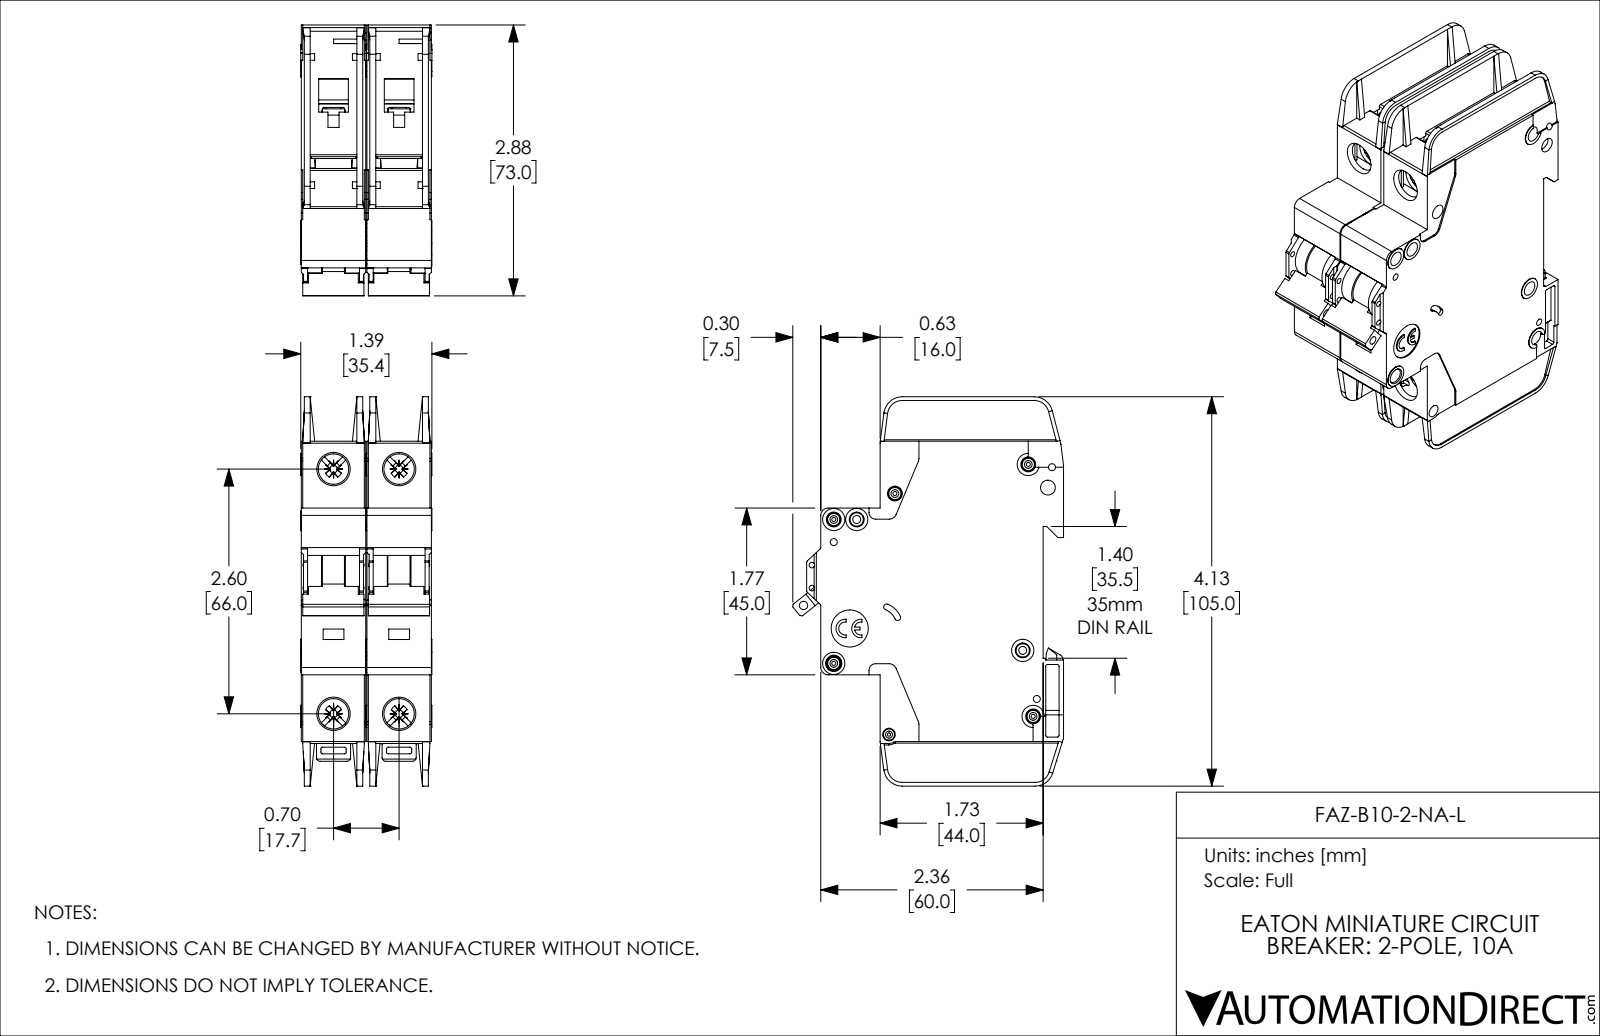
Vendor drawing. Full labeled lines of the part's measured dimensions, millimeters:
Part name (STEP PRODUCT): FAZ-B10-2-NA-L
STEP written by: SolidWorks 2019 (AUTOMOTIVE_DESIGN)
Units: millimetres
Bodies: 2 solids, 2254 faces (1342 planar, 714 cylindrical, 198 other)
Overall size (bounding box): 105 × 73.1 × 35.4
Volume: 153 500 mm³ · Surface area: 52 910 mm²
Round holes (diameter × count): ⌀4 ×8, ⌀1.1 ×5, ⌀1.9 ×4, ⌀8.2 ×4, ⌀1.5 ×2, ⌀2.2 ×2, ⌀0.9 ×1, ⌀2.3 ×1, ⌀2.5 ×1, ⌀3.4 ×1, ⌀10 ×1
Round bosses / shafts (diameter × count): ⌀3.3 ×5, ⌀6 ×4, ⌀3 ×3, ⌀2.5 ×2
Partial cylindrical surfaces — rounded edges, fillets, slot ends (radius × count): R0.5 ×57, R0.4 ×20, R1 ×14, R2 ×10, R1.1 ×8, R0.2 ×5, R5 ×5, R0.3 ×4
Main face-to-face distances: 17.7, 1.2, 17.4, 15, 2.4, 16.2, 13.8, 35.1, 18.9, 16.5
Hole centre spacings: 6.2, 13.6, 17.7, 22.1, 66, 68.3, 4.8, 5.1
